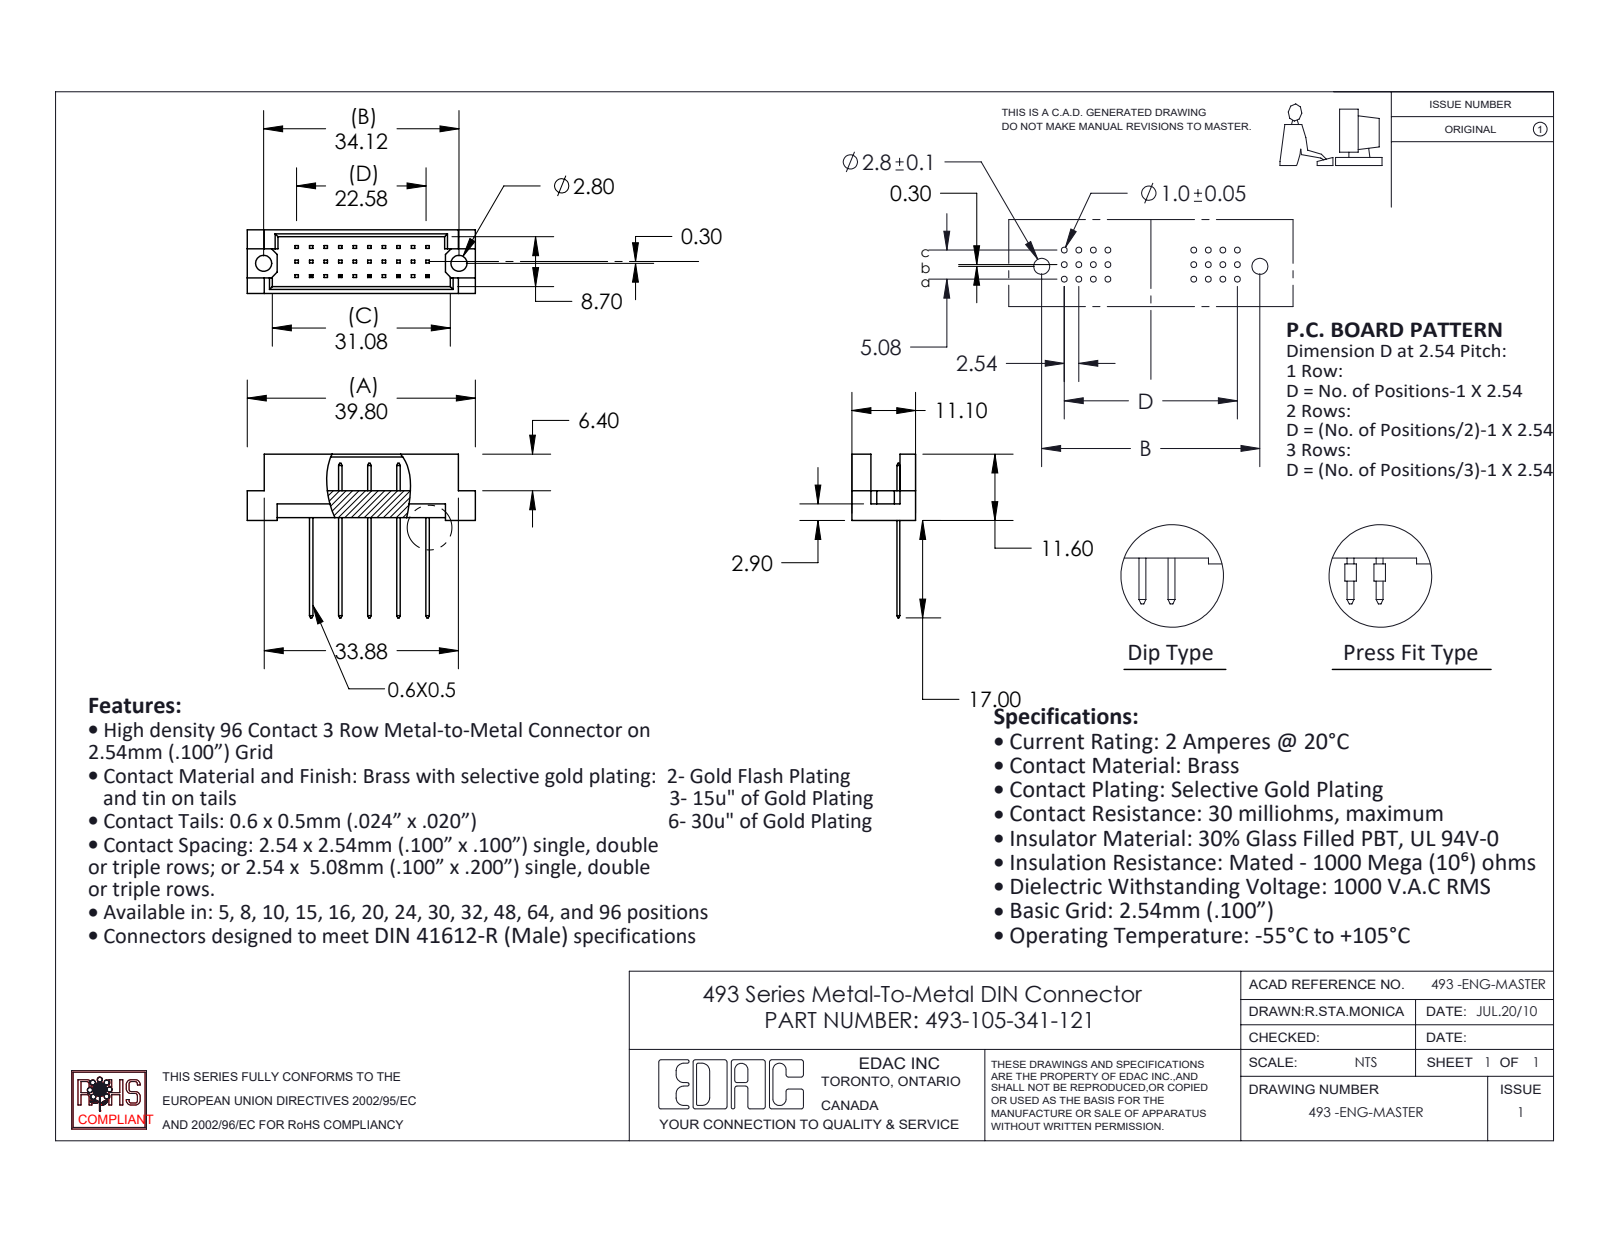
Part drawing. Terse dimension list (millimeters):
name: 493-290_41; 493-105-341-121; 493 Part_30
written by: SolidWorks 2020 (CONFIG_CONTROL_DESIGN)
unit: mm
bodies: 6 solids, 242 faces (238 planar, 4 cylindrical, 0 other)
size: 39.8 × 28.6 × 11.1
volume: 2 413 mm³; area: 3 033 mm²
holes: 2× ⌀2.8
face distances: 1.2, 9.9, 11.1, 8.7, 0.5, 5.08, 4.7, 2.76, 3.26, 7.84
hole spacings: 34.12
